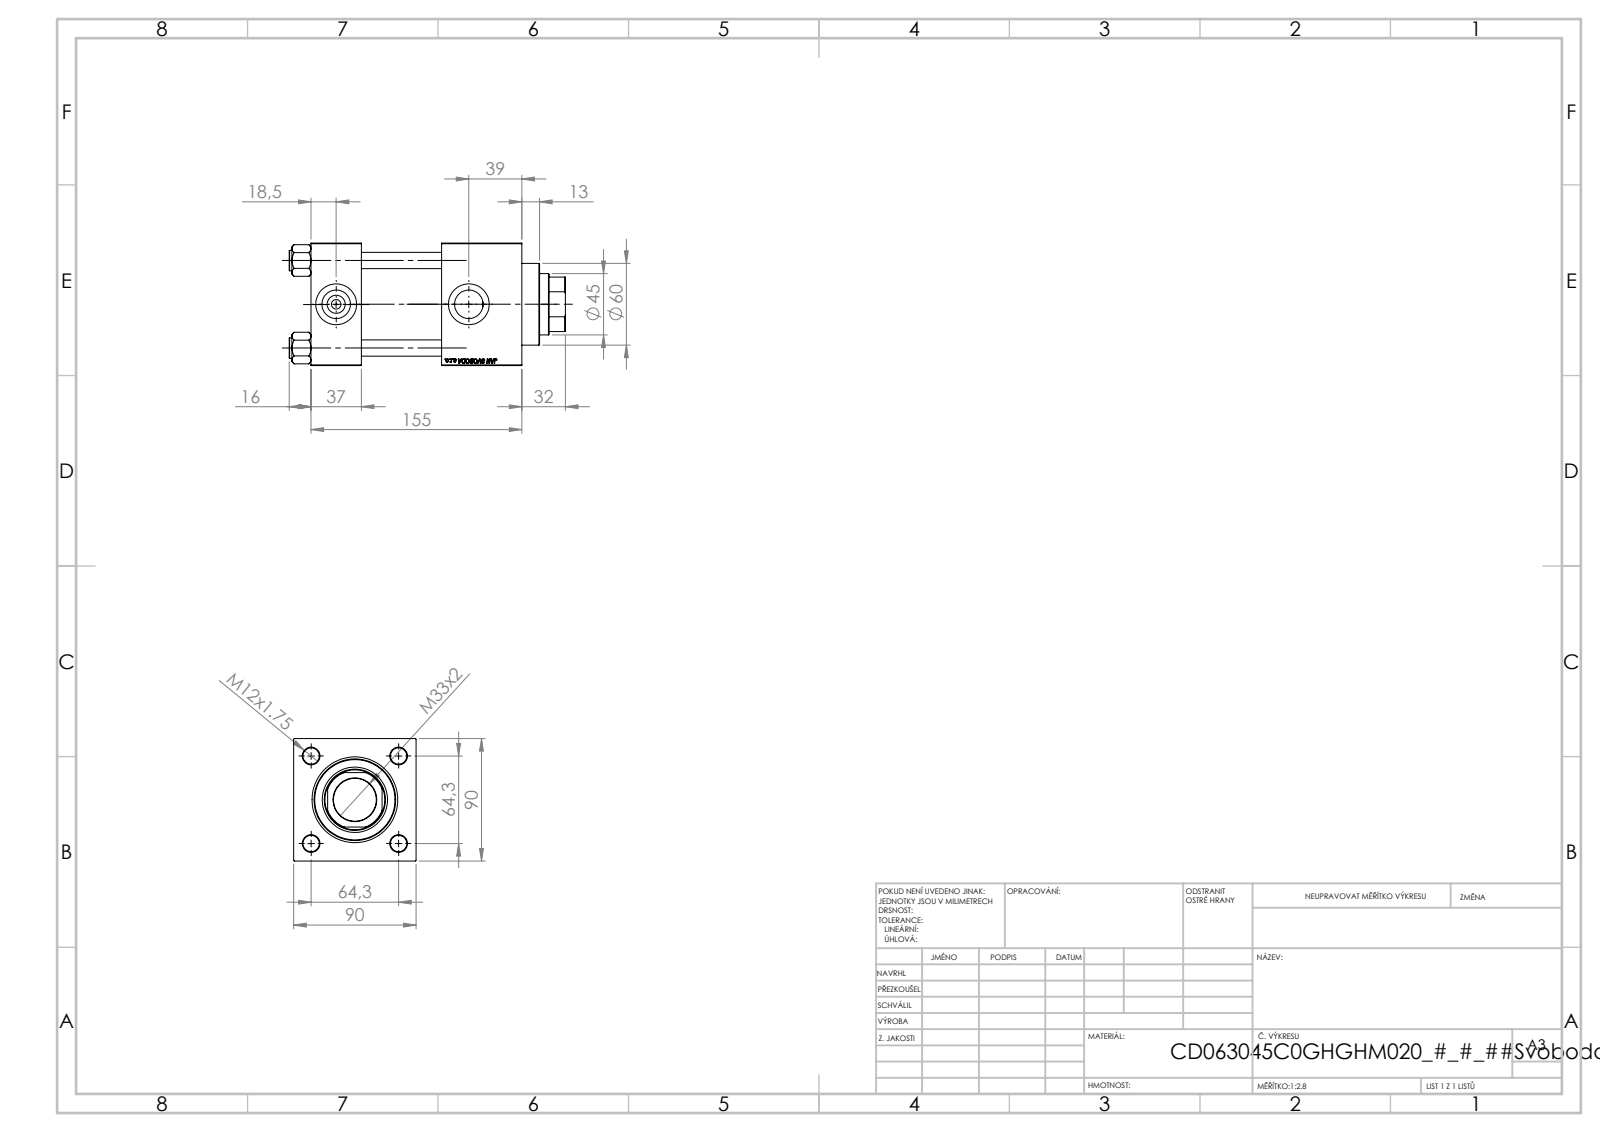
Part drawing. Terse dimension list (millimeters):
name: V215CD_VCP_C; NUT_M5_V215CD_C; V215CD_C_TYCINKA; V215CD_VC_C (+1 more)
written by: SolidWorks 2019 (CONFIG_CONTROL_DESIGN)
unit: mm
bodies: 11 solids, 1145 faces (525 planar, 84 cylindrical, 536 other)
size: 203 × 90 × 90
volume: 954 876 mm³; area: 181 962 mm²
holes: 4× ⌀12, 2× ⌀7, 2× ⌀20.96, 2× ⌀30, 1× ⌀31.5, 1× ⌀45, 1× ⌀48, 1× ⌀50, 1× ⌀60, 1× ⌀63
bosses: 4× ⌀15, 1× ⌀69
rounds: 1× R22
face distances: 90, 37, 155, 118, 126.3, 89.3, 28.7, 76, 39, 50.3
hole spacings: 45.47, 64.3, 90.93, 97.5
